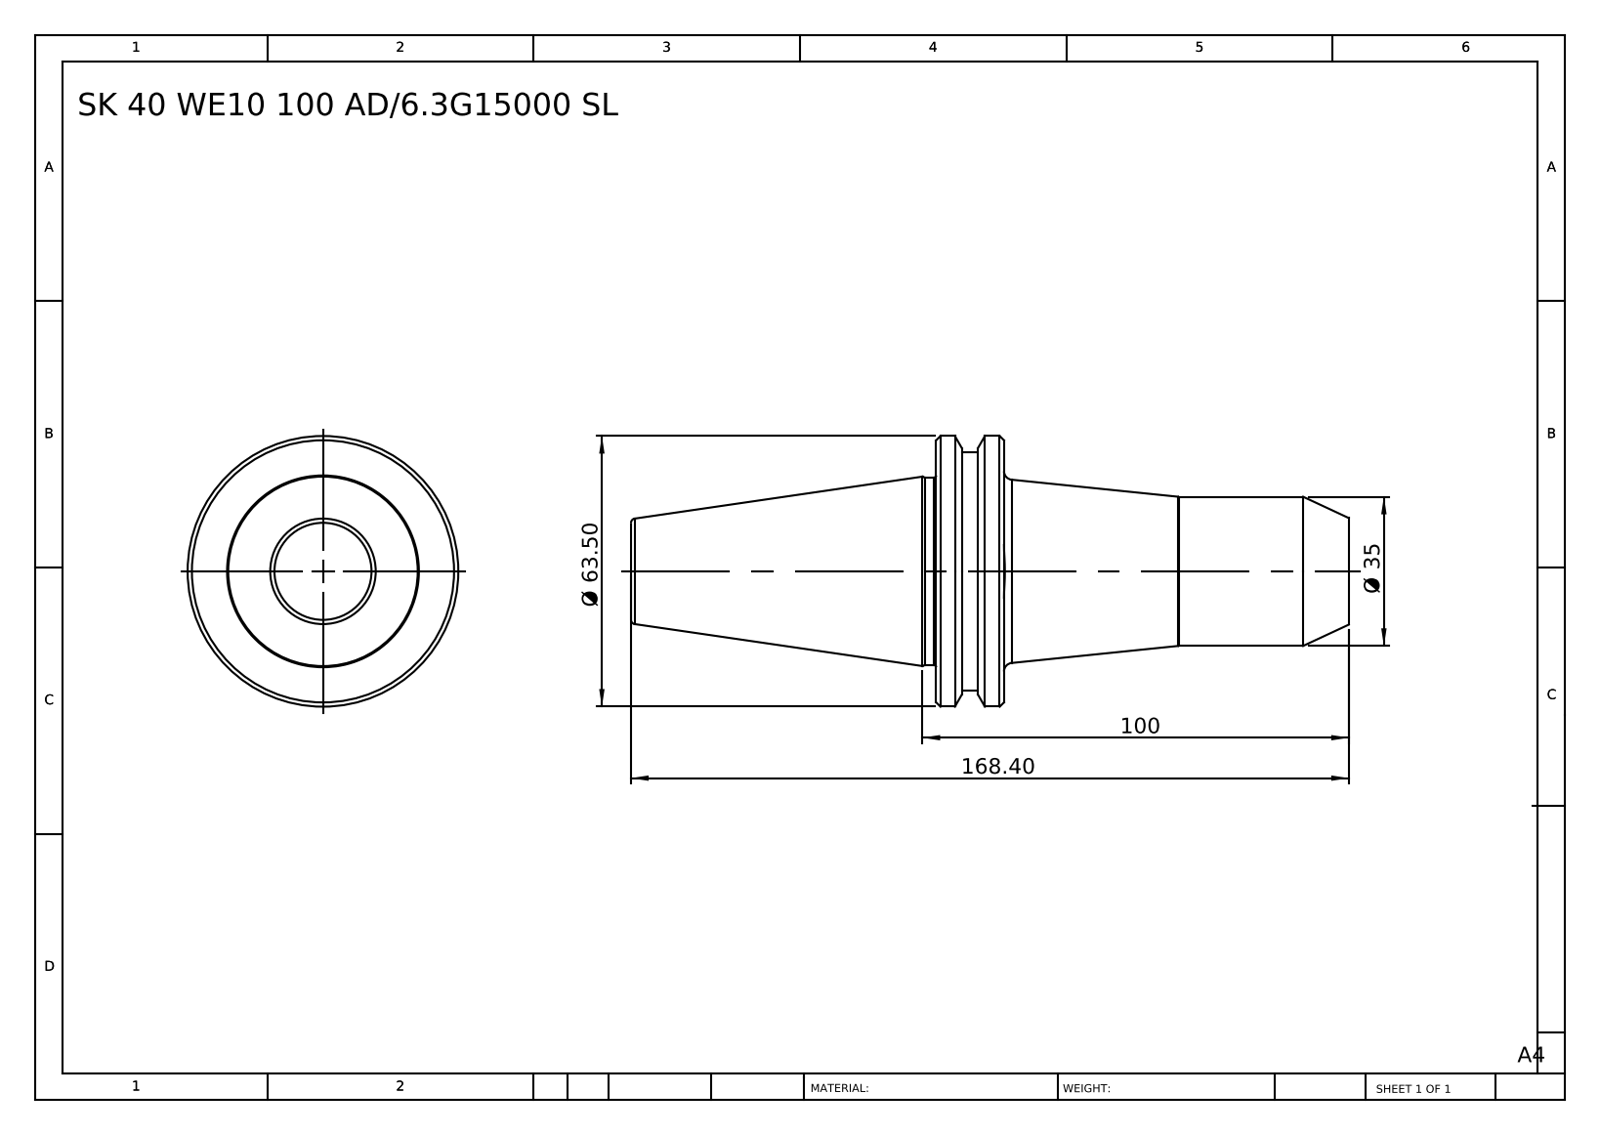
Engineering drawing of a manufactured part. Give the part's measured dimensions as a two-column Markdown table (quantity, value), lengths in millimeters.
| quantity | value |
| --- | --- |
| part name | SK40 WE10 100 AD-6.3G15000 SL |
| STEP written by | SolidWorks 2014 (CONFIG_CONTROL_DESIGN) |
| units | millimeters |
| bodies | 1 solid, 41 faces (7 planar, 10 cylindrical, 24 other) |
| overall size | 168.4 × 63.5 × 63.5 |
| volume | 202 524 mm³ |
| surface area | 25 262 mm² |
| round bosses / shafts (diameter × count) | 63.5 × 1, 56 × 1, 44 × 1, 35 × 1 |
| main face-to-face distances | 15.9, 80.9, 96.8, 168.4, 87.5, 71.6, 87, 6.1, 9.8, 81.4 |
